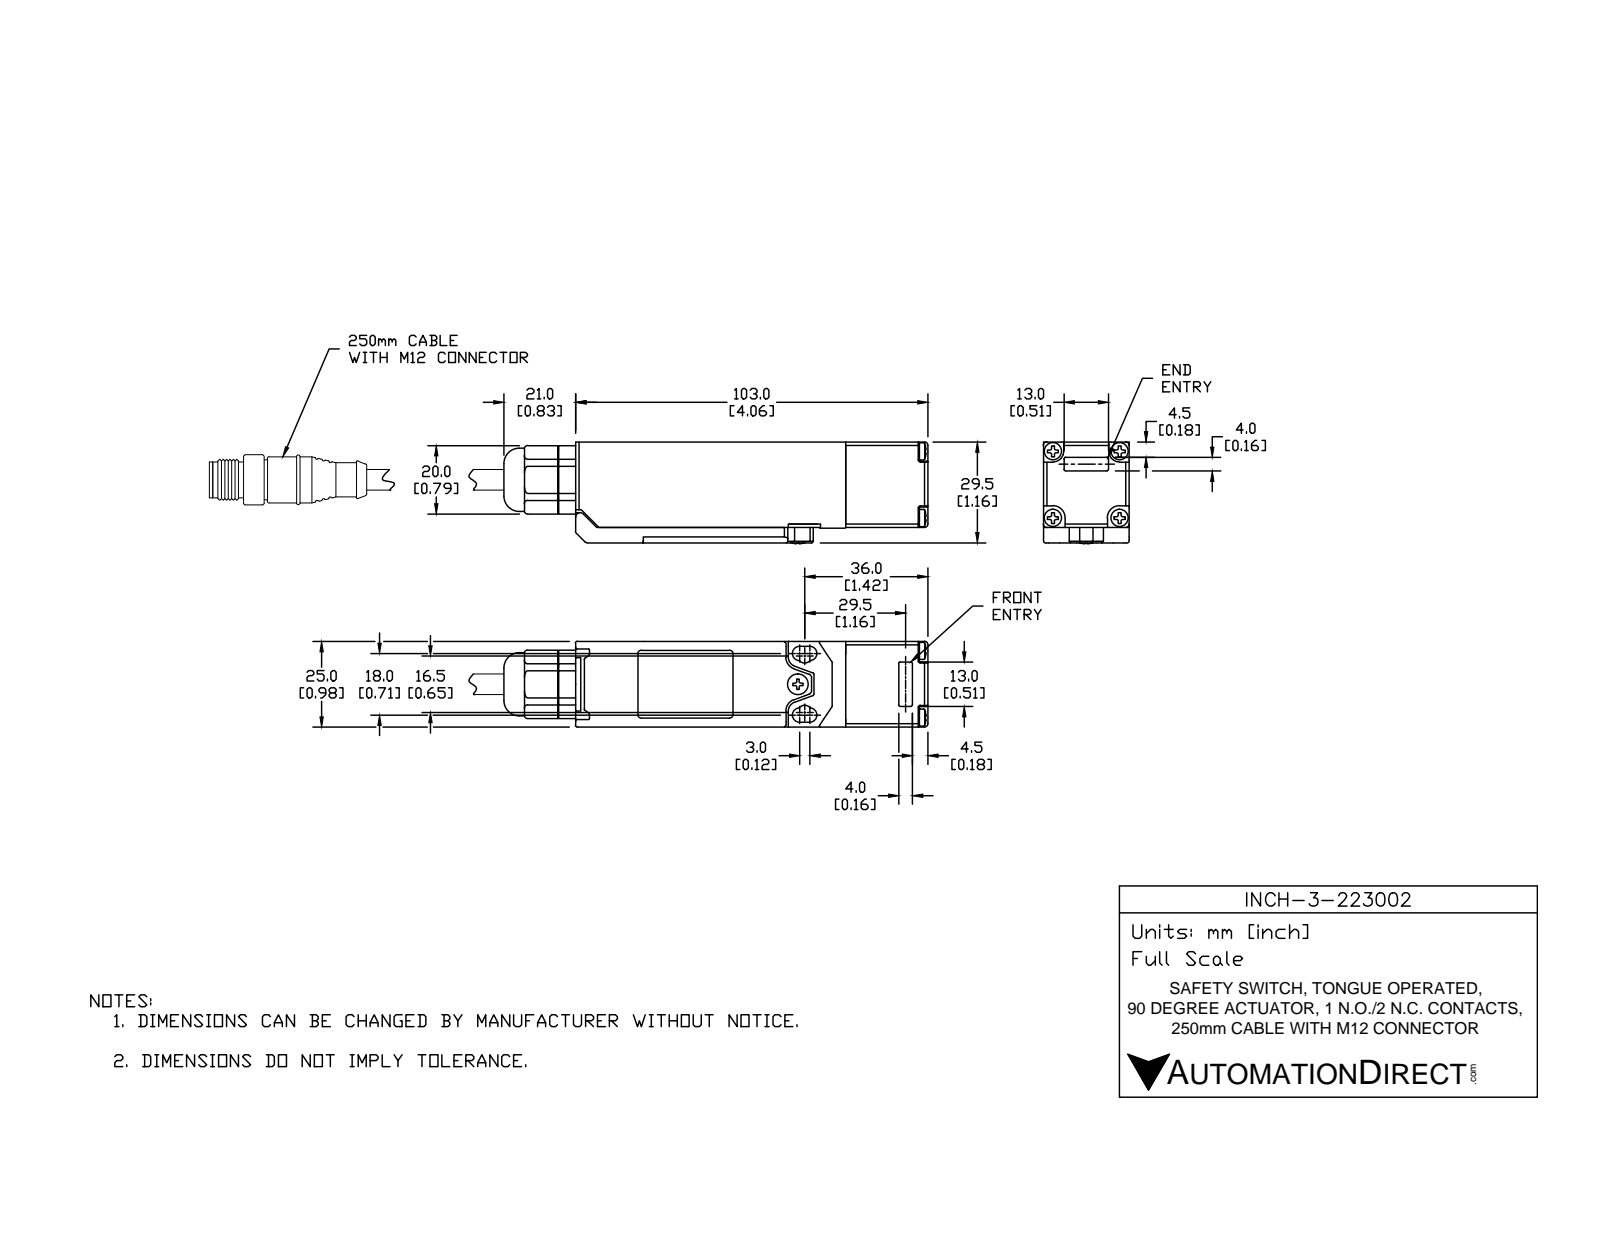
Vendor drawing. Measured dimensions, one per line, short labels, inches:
name: INCH-3-223002
written by: SolidWorks 2014 (AUTOMOTIVE_DESIGN)
unit: in
bodies: 12 solids, 1860 faces (865 planar, 591 cylindrical, 404 other)
size: 4.055 × 1.172 × 0.984
volume: 1.717 in³; area: 47.09 in²
holes: 5× ⌀0.126, 4× ⌀0.094, 2× ⌀0.059, 2× ⌀0.063, 2× ⌀0.071, 2× ⌀0.087, 2× ⌀0.142, 2× ⌀0.63, 1× ⌀0.055, 1× ⌀0.098, 1× ⌀0.102, 1× ⌀0.197
bosses: 5× ⌀0.102, 4× ⌀0.197, 4× ⌀0.079, 2× ⌀0.138, 1× ⌀0.213, 1× ⌀0.118, 1× ⌀0.051
rounds: 209× R0.02, 52× R0.012, 25× R0.039, 24× R0.004, 10× R0.031, 6× R0.083, 6× R0.11, 4× R0.008
face distances: 0.984, 0.079, 0.098, 0.177, 0.906, 0.039, 0.071, 0.913, 0.051, 0.087
hole spacings: 0.543, 0.768, 0.171, 0.187, 0.423, 0.426, 0.45, 0.581
